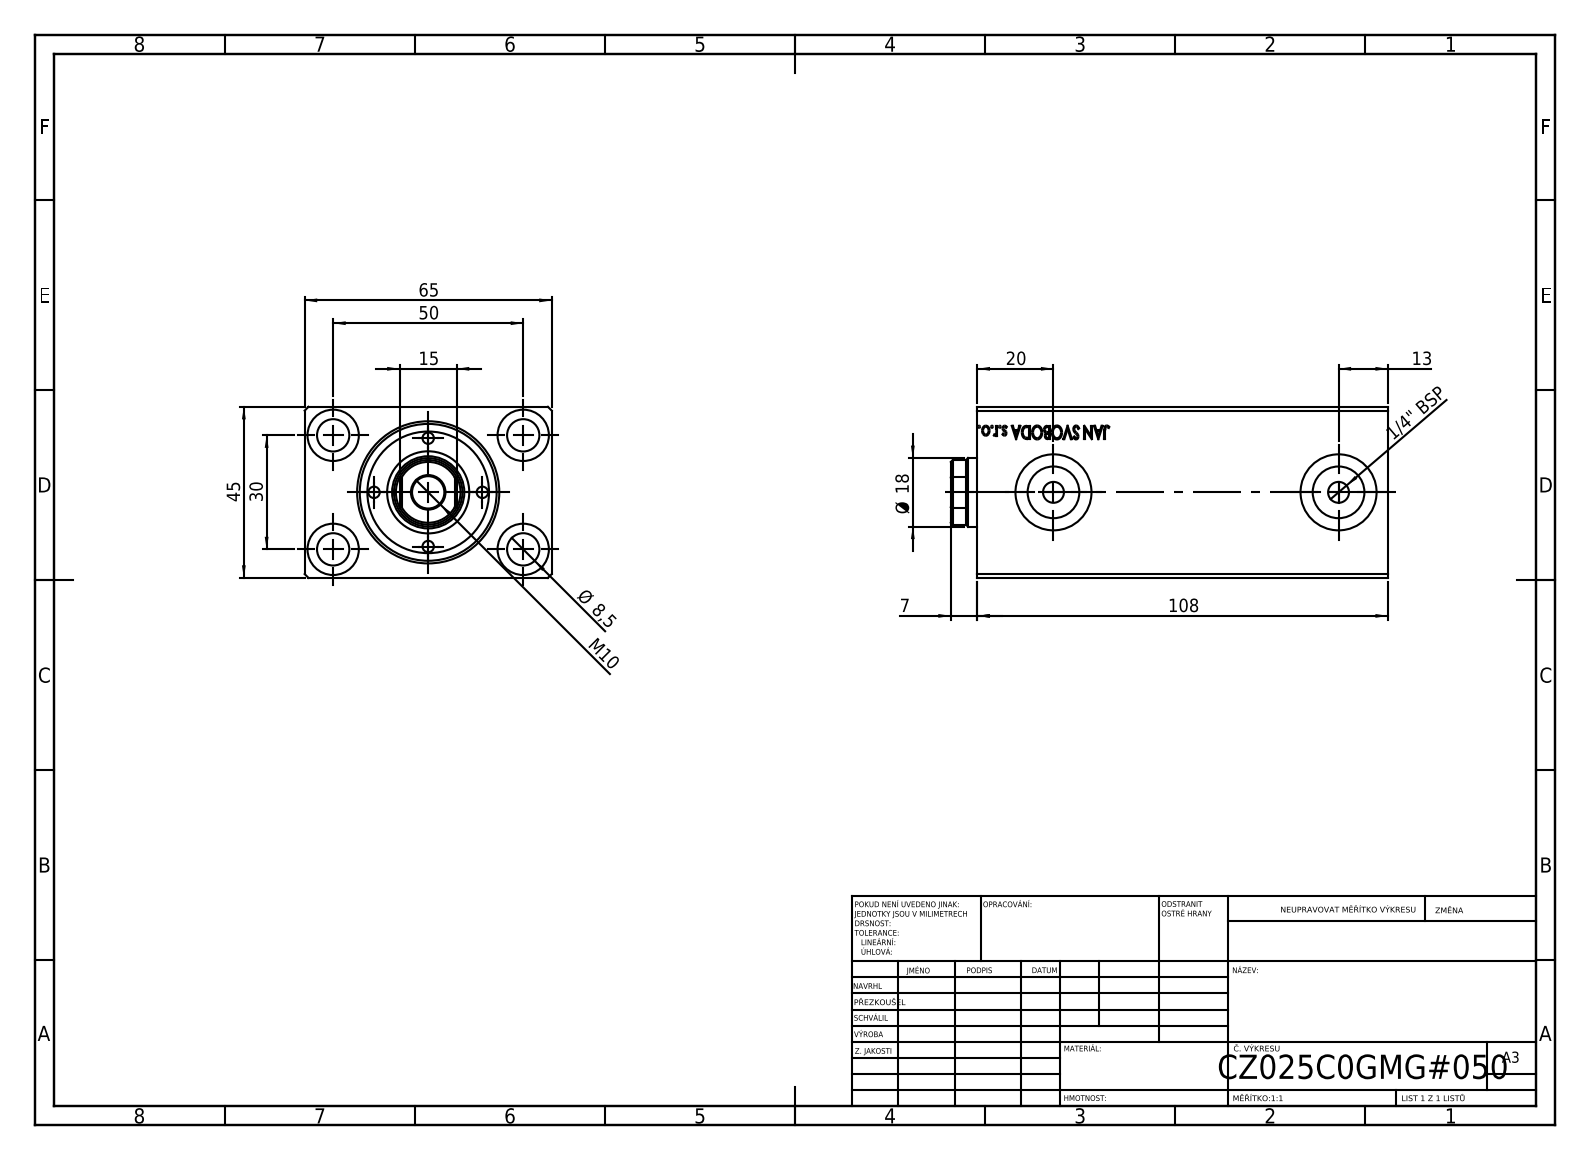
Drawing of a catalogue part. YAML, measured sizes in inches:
step_written_by: "SolidWorks 2019 (CONFIG_CONTROL_DESIGN)"
units: inches
bodies: {solids: 1, faces: 824, planar: 396, cylindrical: 46, other: 382}
overall_size: [4.252, 2.559, 1.772]
volume: 13.98
surface_area: 78.89
round_holes:
  - {diameter: 0.335, count: 4}
  - {diameter: 0.531, count: 4}
  - {diameter: 0.217, count: 2}
  - {diameter: 0.315, count: 2}
  - {diameter: 0.535, count: 2}
  - {diameter: 0.787, count: 2}
  - {diameter: 0.984, count: 1}
  - {diameter: 1.417, count: 1}
face_to_face_distances: [1.772, 2.559, 4.252, 4.244, 0.407, 3.845, 0.276, 3.969, 3.976, 3.748]
hole_center_spacings: [1.148, 1.181, 1.969, 2.296, 2.165, 2.953]
